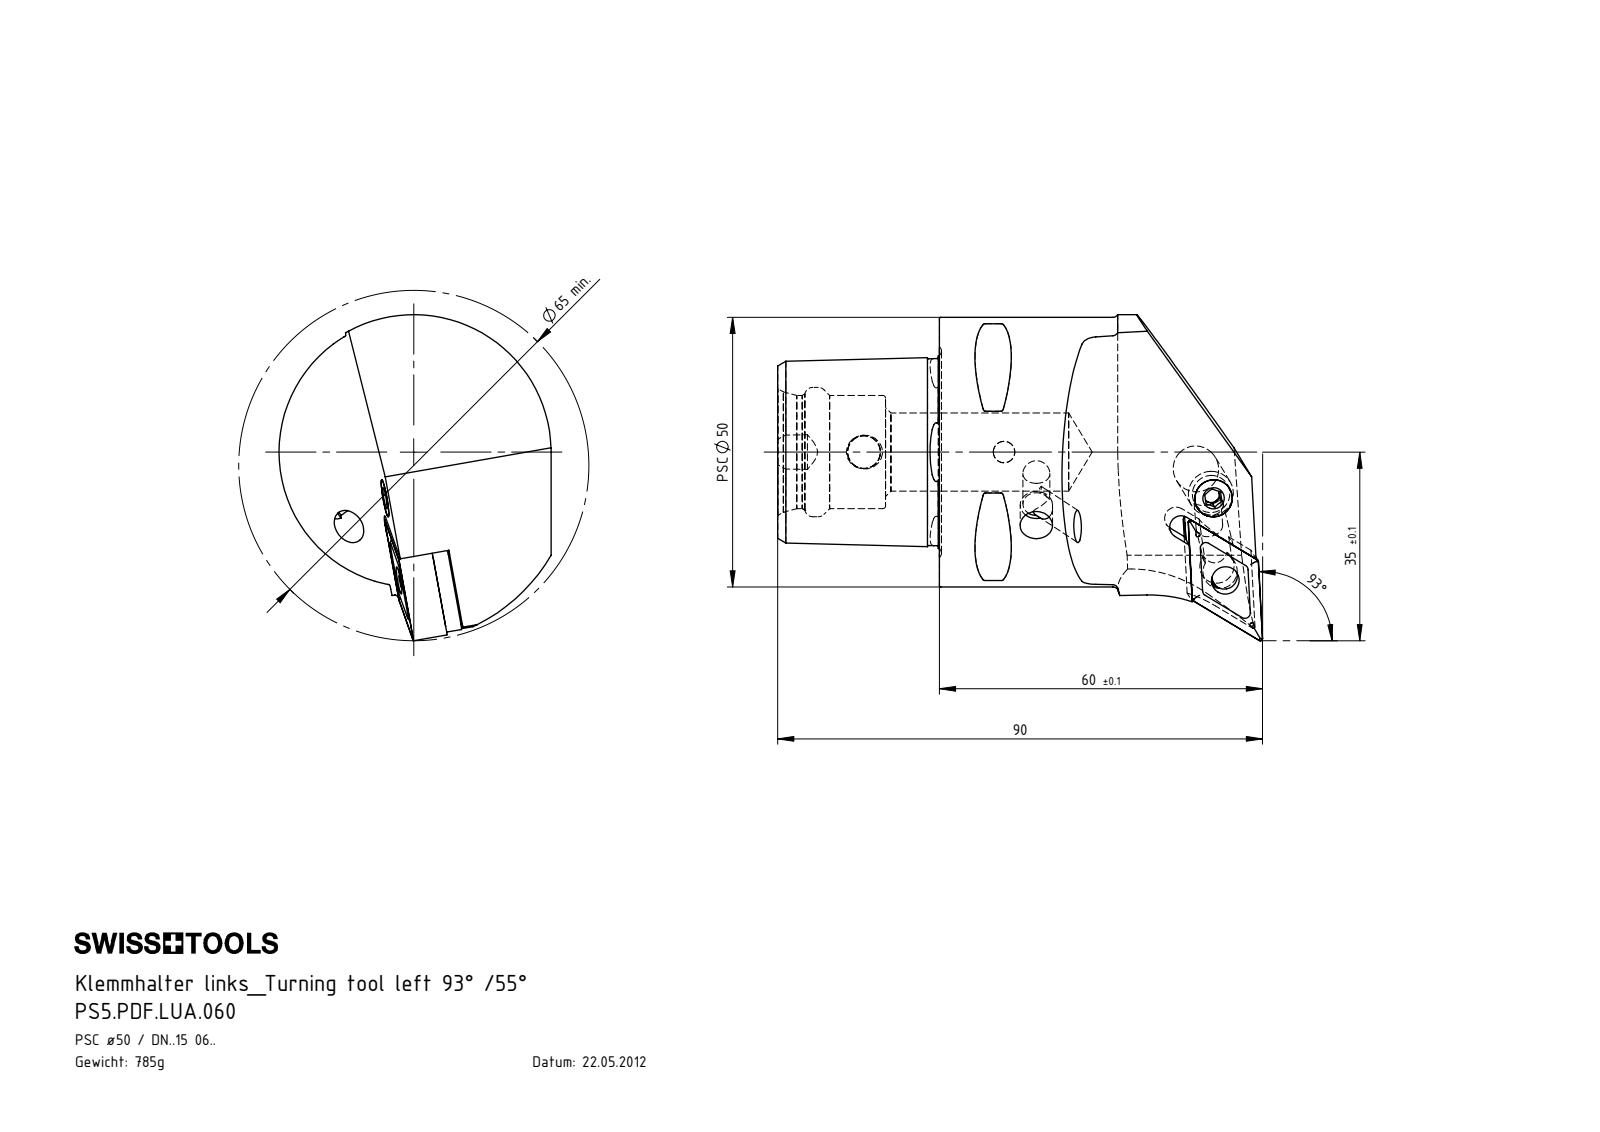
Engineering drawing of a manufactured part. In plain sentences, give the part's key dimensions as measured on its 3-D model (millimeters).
The part is named "PS5-PDF.LUA.060; WDF-ER2.101.003_A; WCD-ER4.101.017_A; WCD-ER1.101.000 (+4 more)". Its 3-D file was written by "SolidWorks 2012 (CONFIG_CONTROL_DESIGN)". It is 8 solids with 335 faces: 92 planar, 81 cylindrical and 162 other. Overall it measures 90 by 60.5 by 50.5 millimeters. Its volume is 100 886 cubic millimeters and its surface area 22 733 square millimeters. Round holes: 3 of diameter 5, 1 of diameter 4, 1 of diameter 5.16, 1 of diameter 6, 1 of diameter 6.1, 1 of diameter 6.4, 1 of diameter 7, 1 of diameter 8.4, 1 of diameter 14.5, 1 of diameter 21, 1 of diameter 24. Round bosses or shafts: 1 of diameter 50, 1 of diameter 8, 1 of diameter 7.9, 1 of diameter 6.4, 1 of diameter 6, 1 of diameter 4.7, 1 of diameter 3.55. Partial cylindrical surfaces (rounded edges, fillets, slot ends): 8 of radius 0.5, 4 of radius 0.4, 4 of radius 1, 2 of radius 2.5, 2 of radius 3.2, 1 of radius 2.1, 1 of radius 2.35, 1 of radius 2.8. The main face-to-face distances are 30, 6.05, 12.34, 19.18, 12.7, 4.85, 3.17, 9.22, 44.4, 3.18. The hole center spacings are 15.6, 15.61, 26.
